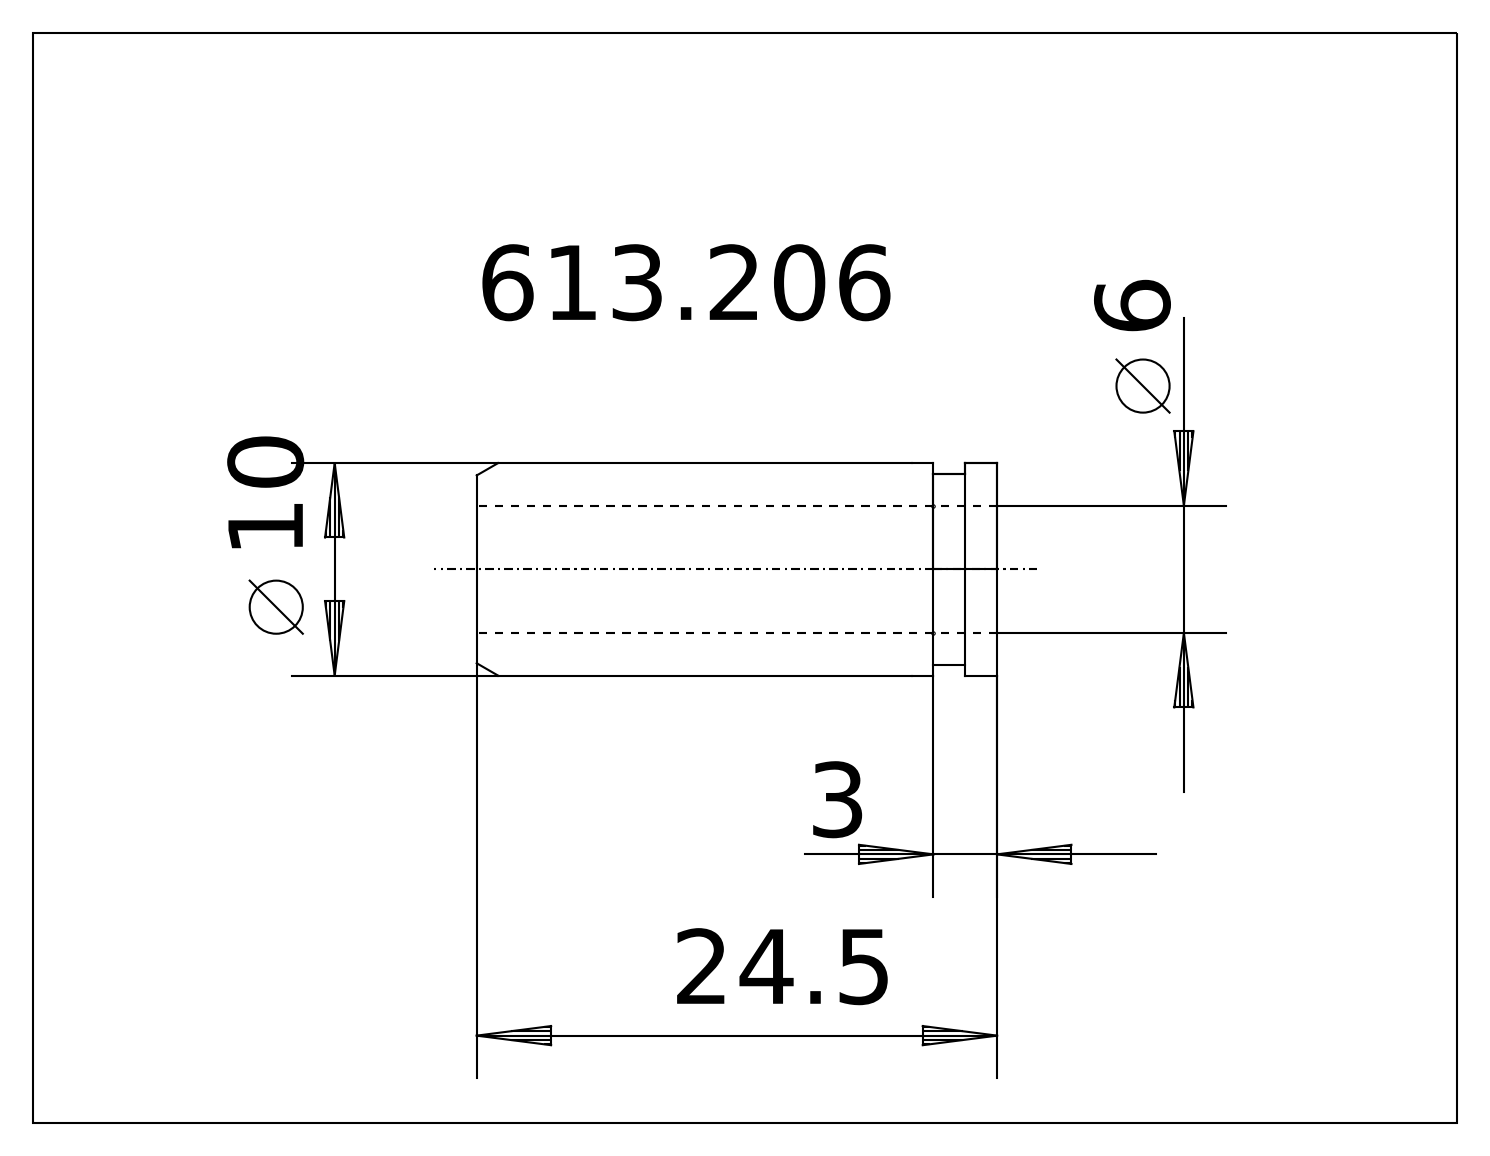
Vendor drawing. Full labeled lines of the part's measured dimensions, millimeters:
STEP written by: ACIS (automotive_design)
Units: millimetres
Bodies: 1 solid, 18 faces (4 planar, 8 cylindrical, 6 other)
Overall size (bounding box): 24.5 × 10 × 10
Volume: 1 195 mm³ · Surface area: 1 329 mm²
Round holes (diameter × count): ⌀6 ×1
Round bosses / shafts (diameter × count): ⌀10 ×1, ⌀9 ×1
Main face-to-face distances: 1.5, 24.5, 3, 21.5, 23
